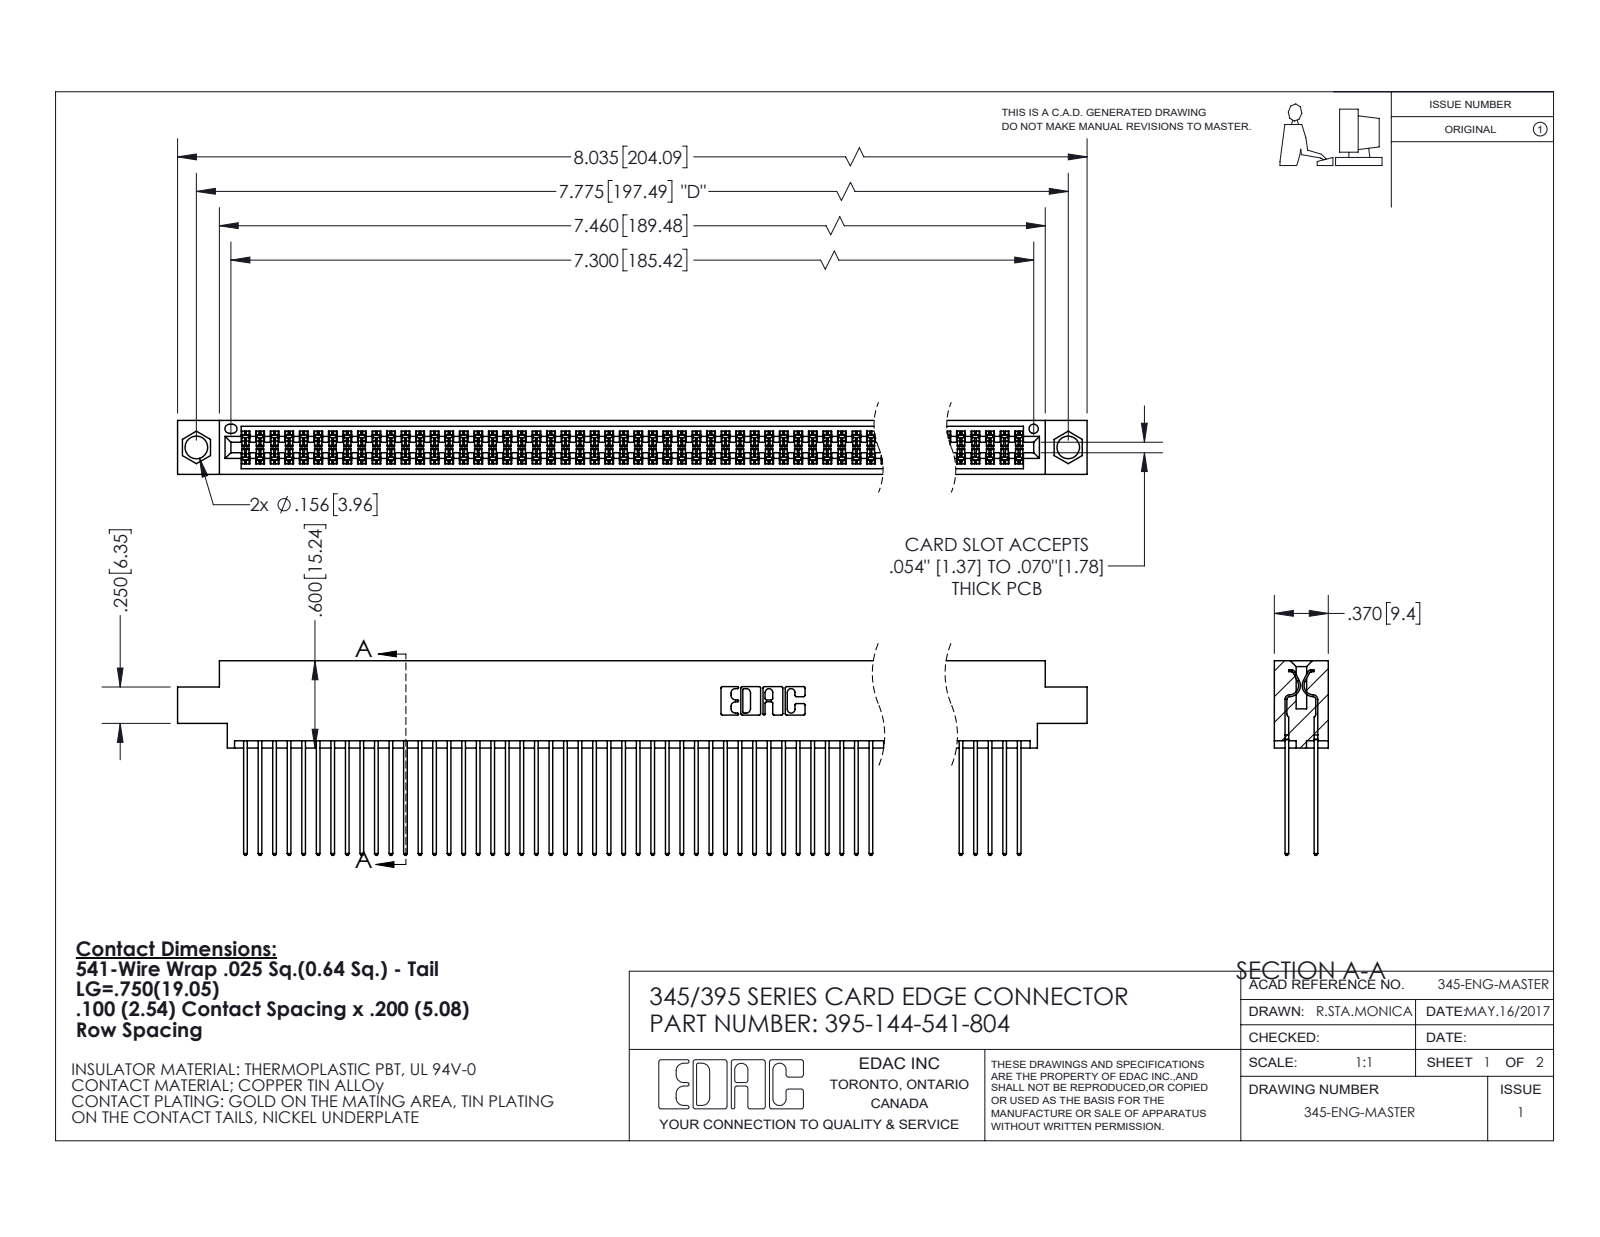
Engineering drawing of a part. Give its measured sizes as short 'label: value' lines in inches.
name: 395-144-541-804; 345-292-001_345-293-141; 345 Part_0.170 Offset - 0.156 Dia-TI
written by: SolidWorks 2020 (CONFIG_CONTROL_DESIGN)
unit: in
bodies: 145 solids, 7344 faces (4850 planar, 2494 cylindrical, 0 other)
size: 8.035 × 1.337 × 0.37
volume: 1.264 in³; area: 54.36 in²
holes: 2× ⌀0.156, 1× ⌀0.064
rounds: 216× R0.006, 144× R0.01, 22× R0.01, 6× R0.007, 6× R0.031, 3× R0.026, 2× R0.014, 2× R0.019
face distances: 0.072, 0.298, 0.2, 0.098, 0.272, 0.025, 0.225, 0.37, 0.175, 0.149
hole spacings: 0.27, 7.539, 7.775
